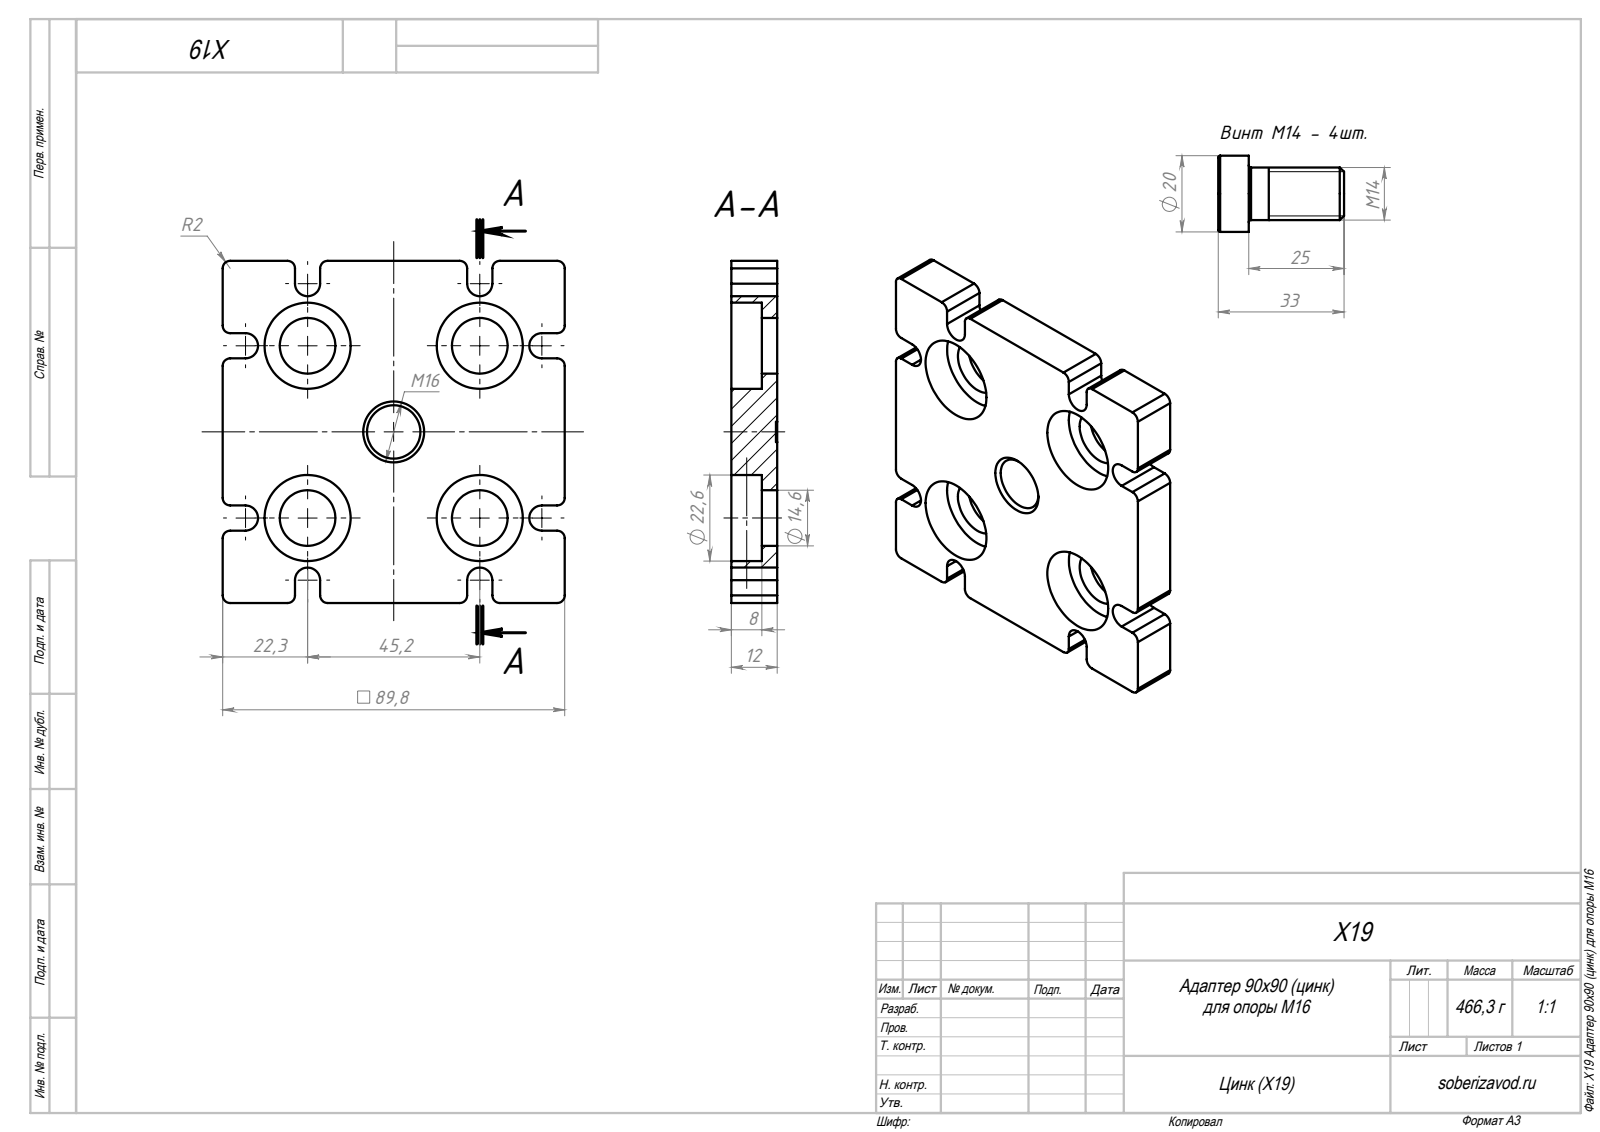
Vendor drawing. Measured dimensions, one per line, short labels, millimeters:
name: X19 Адаптер 90х90 (цинк) для опоры М16; X19 Адаптер 90х90 (цинк) для опоры М16_00
written by: SolidWorks 2018 (AUTOMOTIVE_DESIGN)
unit: mm
bodies: 5 solids, 202 faces (86 planar, 88 cylindrical, 28 other)
size: 89.8 × 89.8 × 33
volume: 96 505 mm³; area: 32 671 mm²
holes: 12× ⌀6, 4× ⌀14.6, 4× ⌀22.6, 1× ⌀14
bosses: 4× ⌀21, 4× ⌀14
rounds: 20× R2, 8× R3.3
face distances: 12, 89.8, 4, 8, 45.2, 6.6, 5.5, 1.5, 6.5, 19
hole spacings: 22.64, 51.79, 19.47, 24, 31.96, 33.94, 35.55, 40.48
